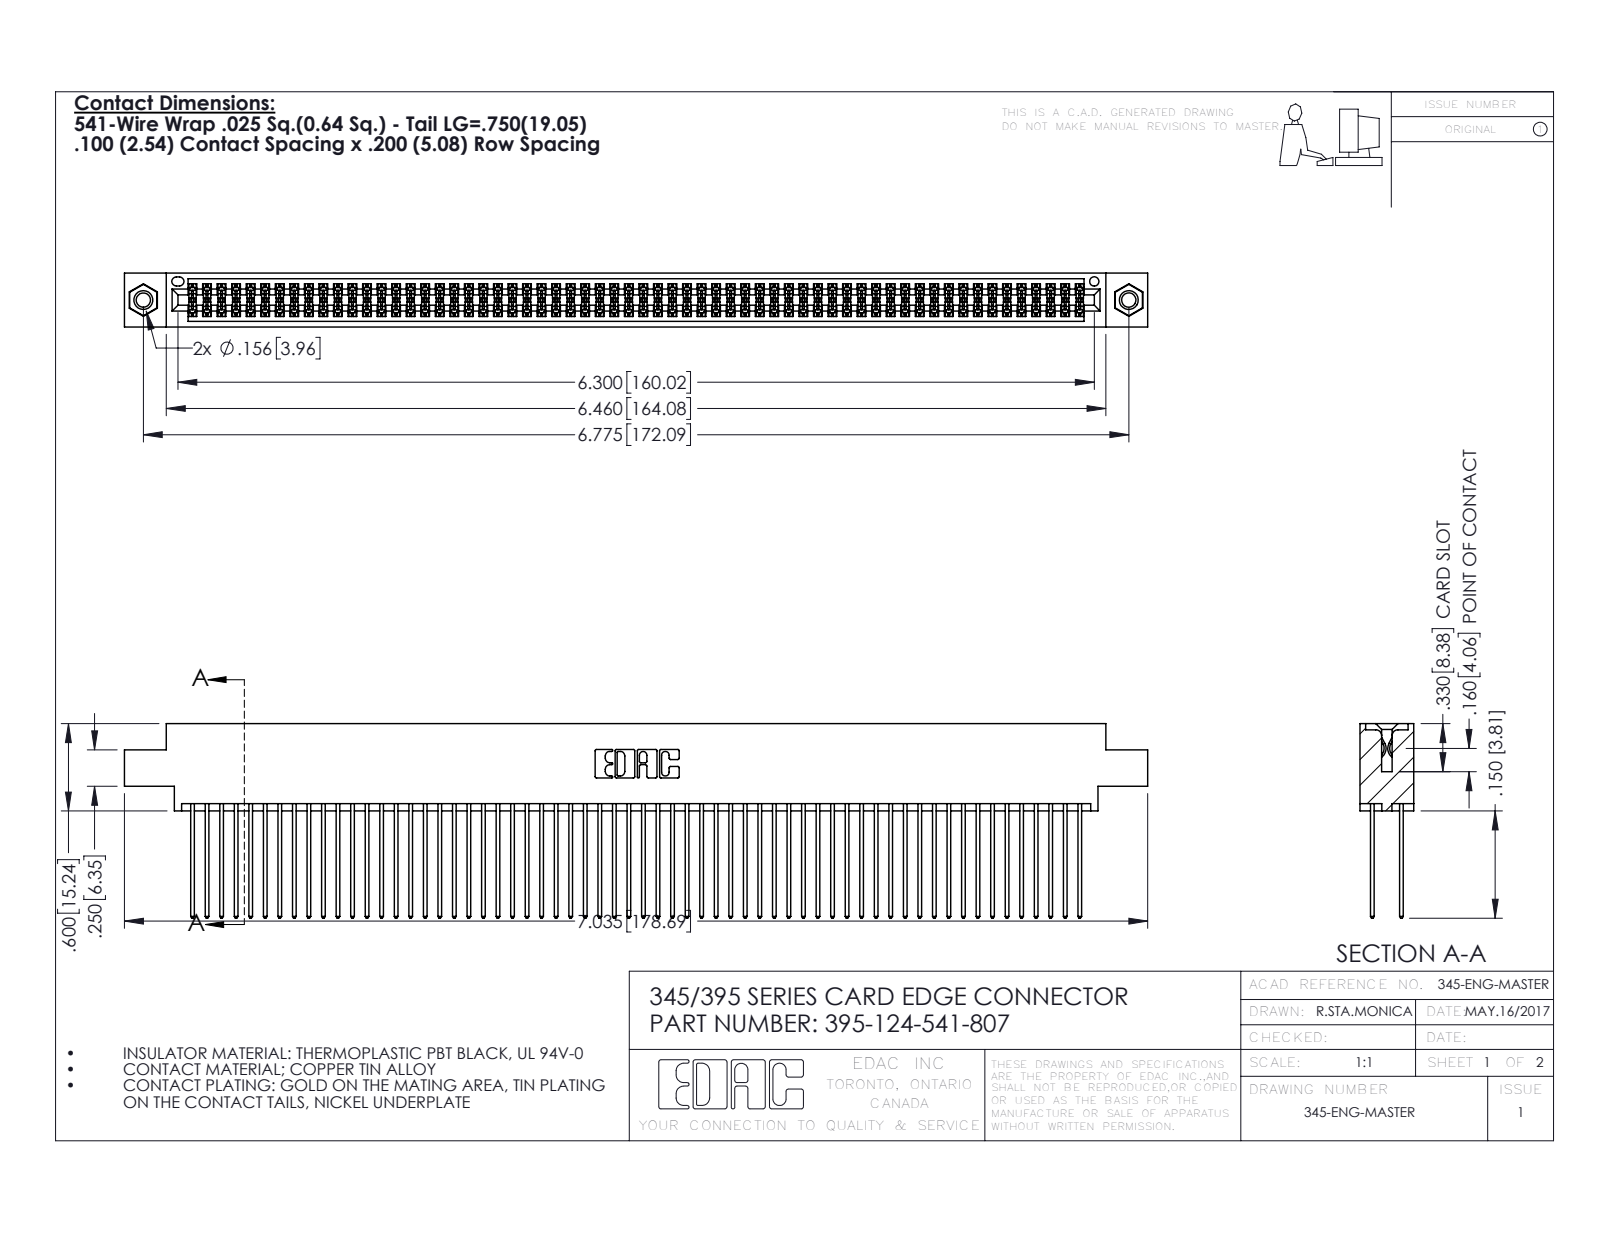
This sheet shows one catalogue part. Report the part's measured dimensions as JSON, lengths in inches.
{"part_name": "345 Part_0.170 Offset - 0.156 Dia-TI; 395-124-541-807; 345-250-001_345-250-005-103; 345-292-001_345-293-141", "step_written_by": "SolidWorks 2016 (CONFIG_CONTROL_DESIGN)", "units": "inches", "bodies": {"solids": 127, "faces": 6390, "planar": 4208, "cylindrical": 2166, "other": 16}, "overall_size": [7.035, 1.337, 0.37], "volume_in3": 1.106, "surface_area_in2": 47.58, "round_holes": [[0.098, 2], [0.125, 2], [0.156, 2], [0.064, 1]], "round_bosses_or_shafts": [[0.155, 2]], "partial_cylinders_radius": [[0.006, 186], [0.01, 124], [0.01, 22], [0.007, 6], [0.031, 6], [0.026, 3], [0.014, 2], [0.019, 2]], "face_to_face_distances": [0.072, 0.298, 0.2, 0.098, 0.272, 0.025, 0.225, 0.37, 0.175, 0.149], "hole_center_spacings": [0.27, 6.539, 6.775]}
